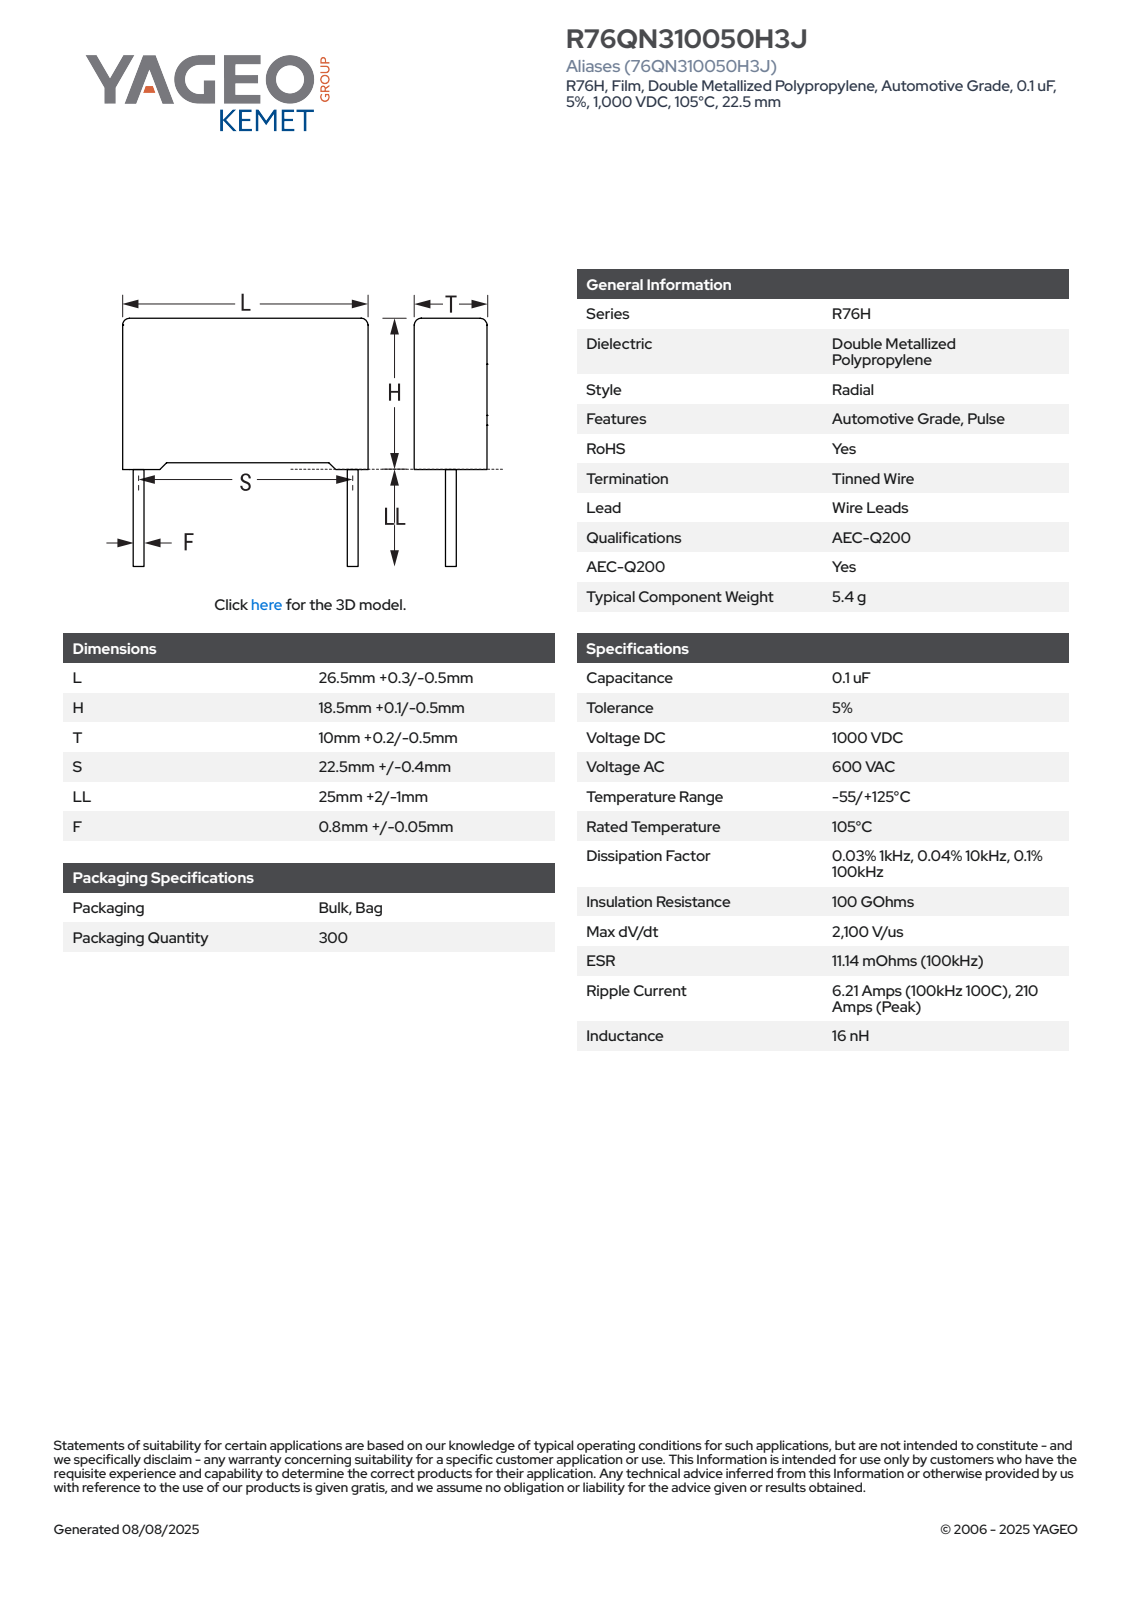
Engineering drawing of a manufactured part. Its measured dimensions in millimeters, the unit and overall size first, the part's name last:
Units: millimetres
Overall size (bounding box): 45.6 × 26.8 × 10.21
Round bosses / shafts (diameter × count): ⌀0.85 ×2
Partial cylindrical surfaces — rounded edges, fillets, slot ends (radius × count): R0.5 ×4
Main face-to-face distances: 10.2, 17.85, 26.8, 17.96, 0.75, 0.64, 18.6, 0.89, 9.31, 25.91
Volume: 4 933 mm³ · Surface area: 2 112 mm²
Bodies: 4 solids, 85 faces (77 planar, 8 cylindrical, 0 other)
Part name (STEP PRODUCT): CFR_RB2R76_26.5X18.5X10_L26.8H18.6T10.2S22.5LL27F0.85
STEP written by: SolidWorks 2014 (AUTOMOTIVE_DESIGN)
